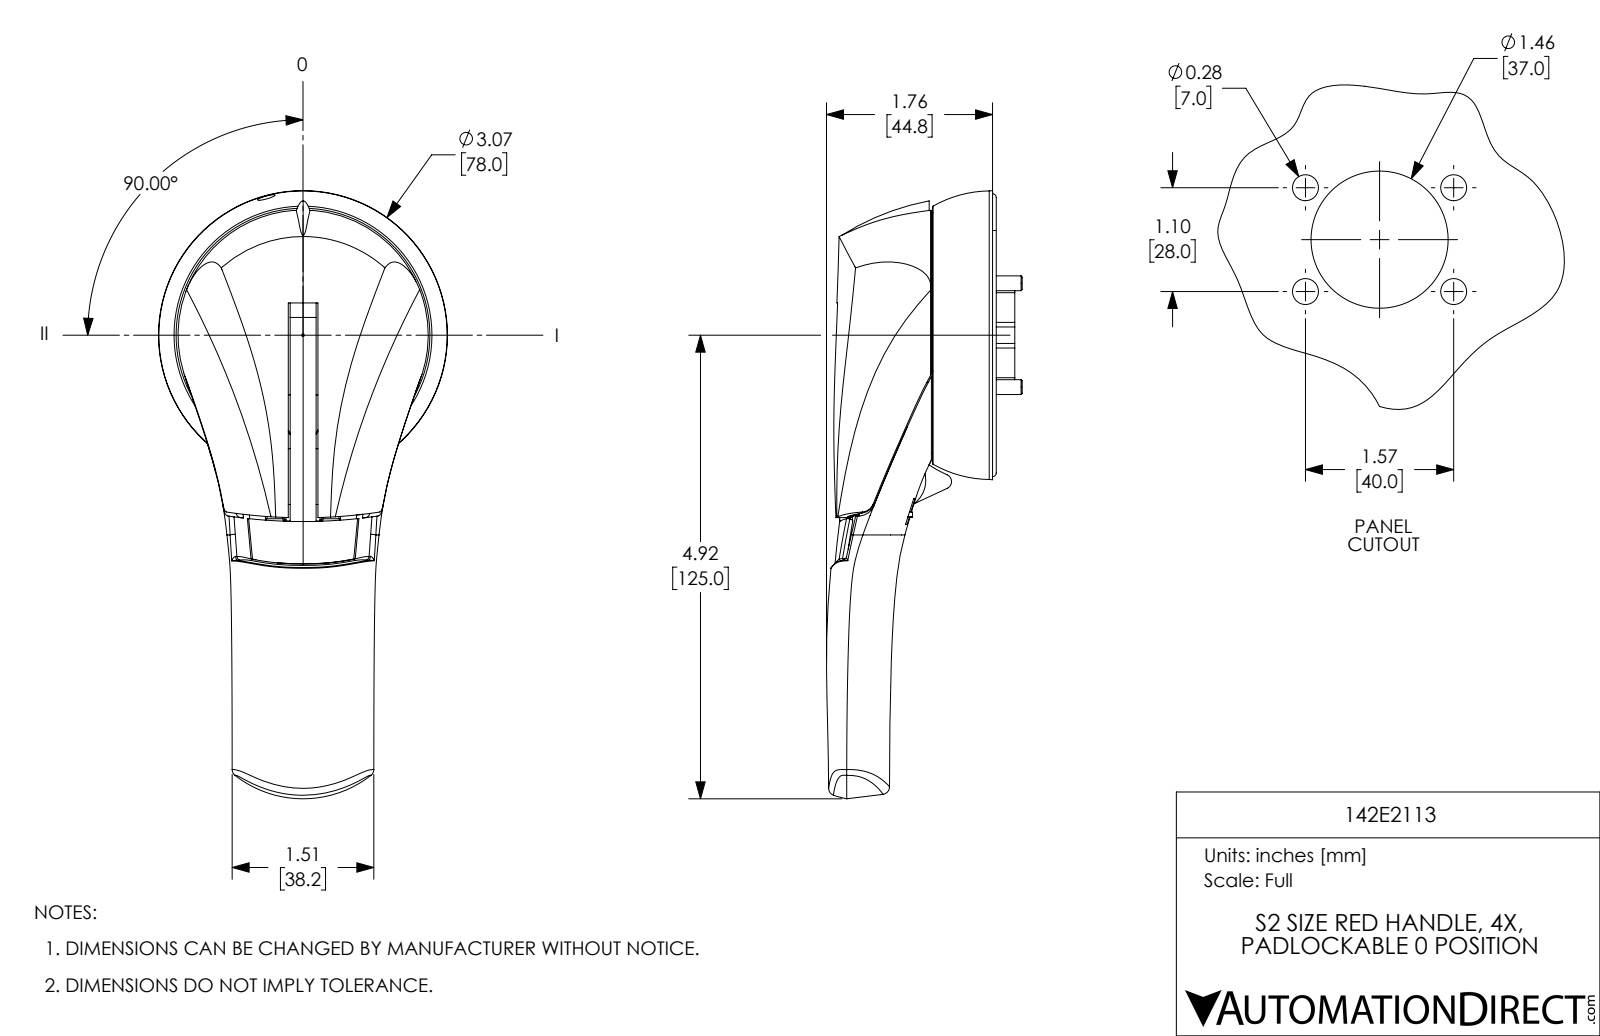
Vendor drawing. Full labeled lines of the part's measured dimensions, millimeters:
Part name (STEP PRODUCT): 142E2113
STEP written by: SolidWorks 2017 (AUTOMOTIVE_DESIGN)
Units: millimetres
Bodies: 8 solids, 1516 faces (810 planar, 548 cylindrical, 158 other)
Overall size (bounding box): 164 × 78 × 52.8
Volume: 155 900 mm³ · Surface area: 56 330 mm²
Round holes (diameter × count): ⌀4 ×6, ⌀8.6 ×4, ⌀10.8 ×4, ⌀0.8 ×3, ⌀4.3 ×2, ⌀9.2 ×2, ⌀3 ×1, ⌀4.8 ×1, ⌀76 ×1
Round bosses / shafts (diameter × count): ⌀0.5 ×11, ⌀8.5 ×4, ⌀8 ×4, ⌀2.3 ×3, ⌀1.8 ×3, ⌀5.8 ×2, ⌀71.6 ×1, ⌀68.6 ×1
Partial cylindrical surfaces — rounded edges, fillets, slot ends (radius × count): R0.3 ×221, R0.4 ×20, R0.9 ×20, R0.8 ×15, R1 ×4, R0.6 ×3, R138.1 ×3, R2 ×2
Main face-to-face distances: 0.6, 17.8, 18.1, 17.5, 0.9, 2.6, 7, 4.4, 6.2, 1.2
Hole centre spacings: 24.4, 7.8, 17, 27.9, 28, 30.6, 40, 47.8
